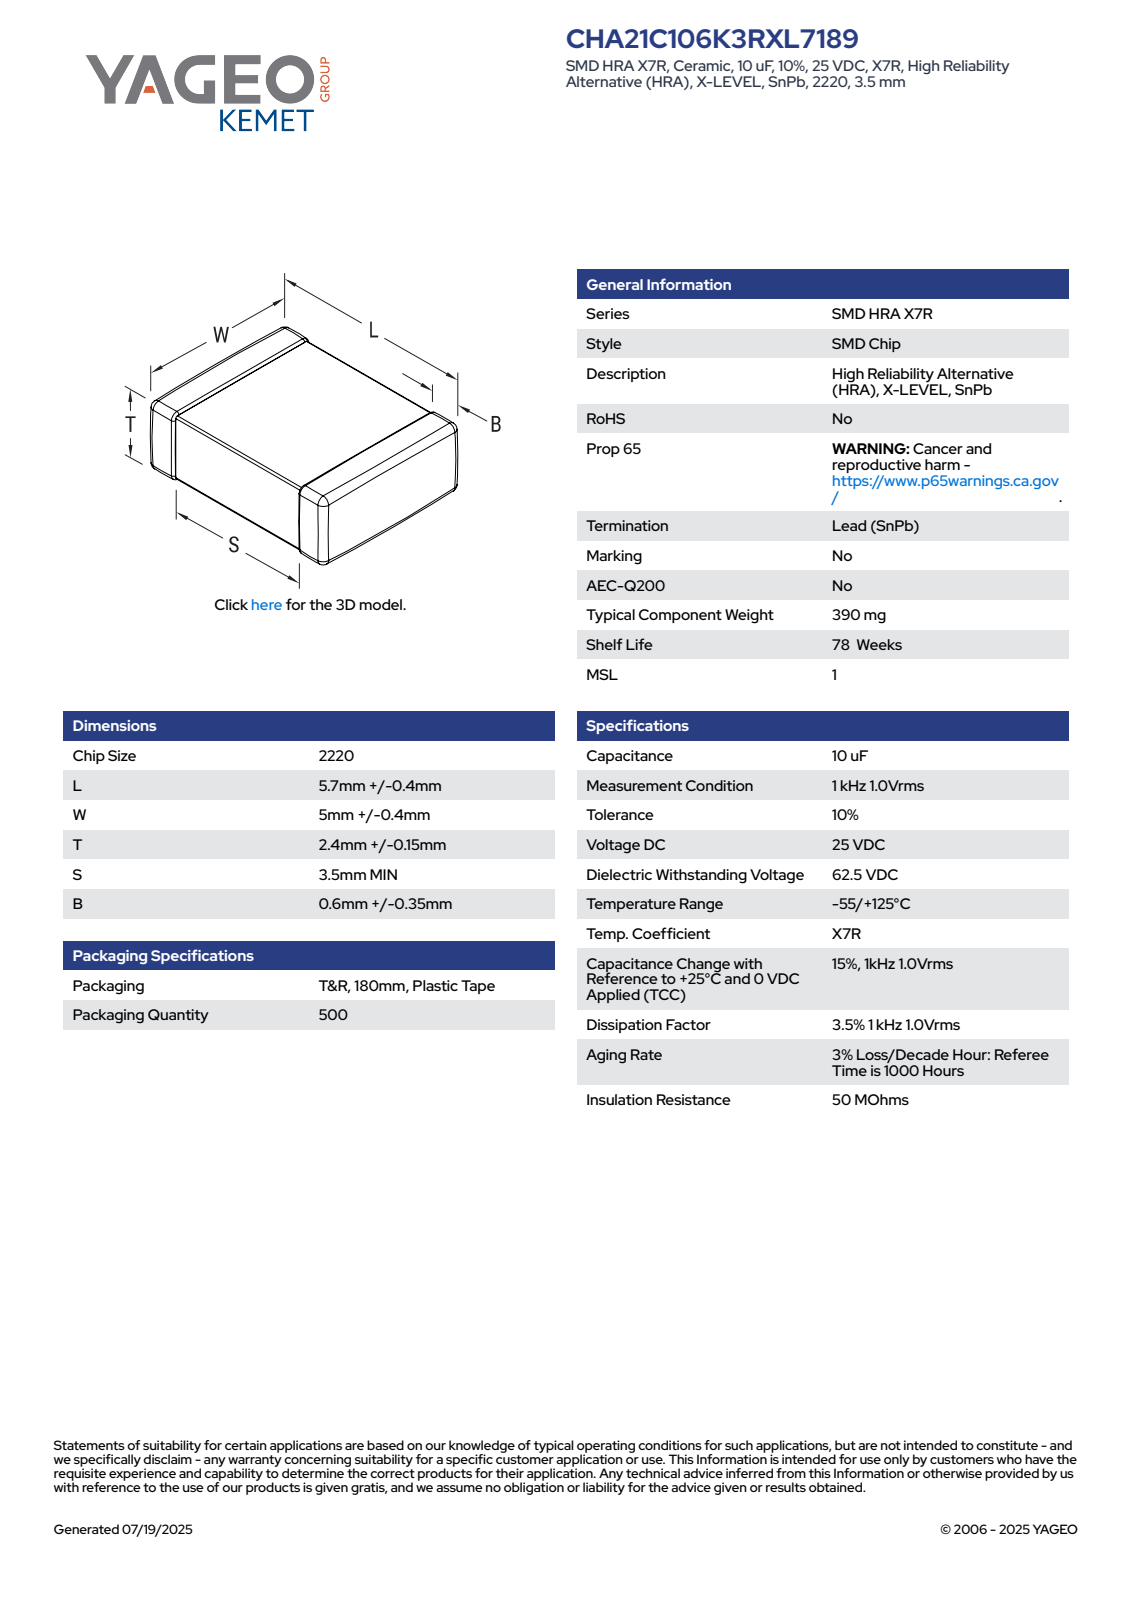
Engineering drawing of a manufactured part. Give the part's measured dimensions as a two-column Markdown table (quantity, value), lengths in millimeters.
| quantity | value |
| --- | --- |
| part name | CCSM_STD_2220_L6.1W5.4T2.55S2.4B0.95 |
| STEP written by | SolidWorks 2021 (AUTOMOTIVE_DESIGN) |
| units | millimeters |
| bodies | 4 solids, 125 faces (71 planar, 38 cylindrical, 16 other) |
| overall size | 6.1 × 5.4 × 2.55 |
| volume | 76 mm³ |
| surface area | 124 mm² |
| partial cylindrical surfaces (radius × count) | 0.11 × 24 |
| main face-to-face distances | 2.33, 2.44, 6.1, 5.18, 2.55, 5.29, 5.4, 2.5, 3.6, 3.29 |
